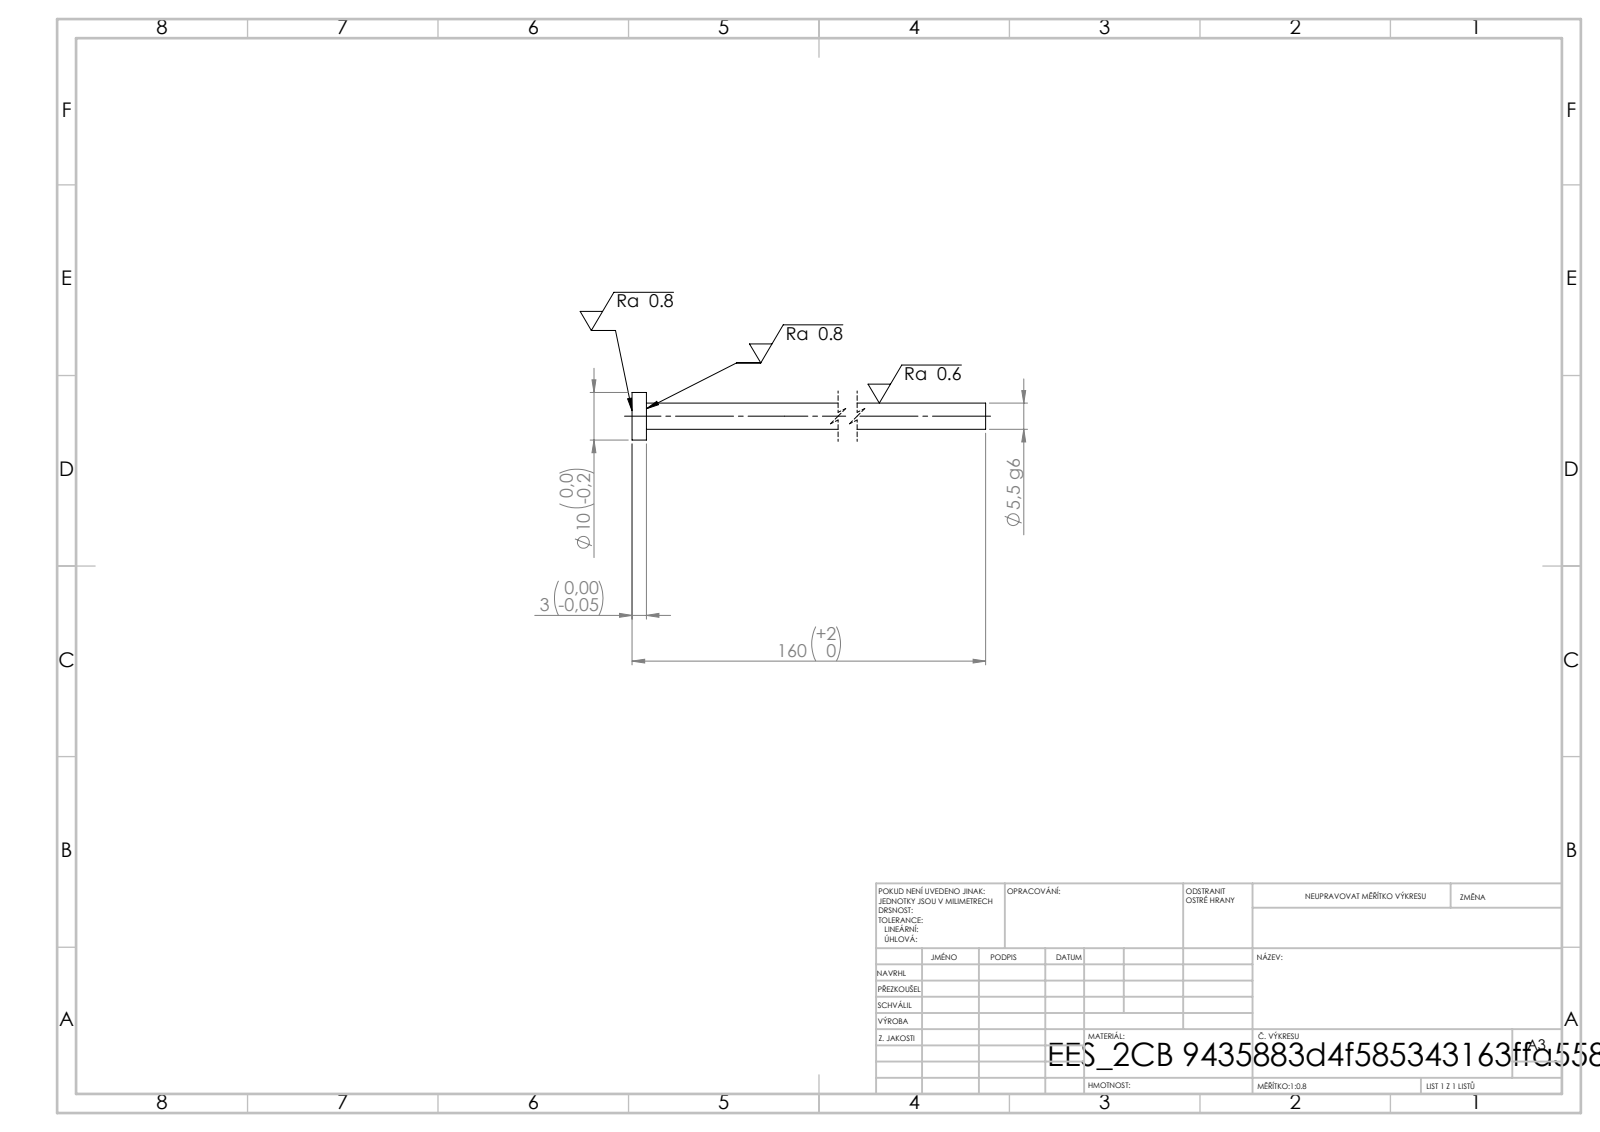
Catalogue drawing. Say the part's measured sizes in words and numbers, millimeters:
Its 3-D file was written by "SolidWorks 2019 (CONFIG_CONTROL_DESIGN)". It is 1 solid with 7 faces: 3 planar, 4 cylindrical and 0 other. Overall it measures 160 by 10 by 10 millimeters. Its volume is 3 966 cubic millimeters and its surface area 2 964 square millimeters. Round bosses or shafts: 1 of diameter 10, 1 of diameter 5.5. The main face-to-face distances are 3, 160, 157.
